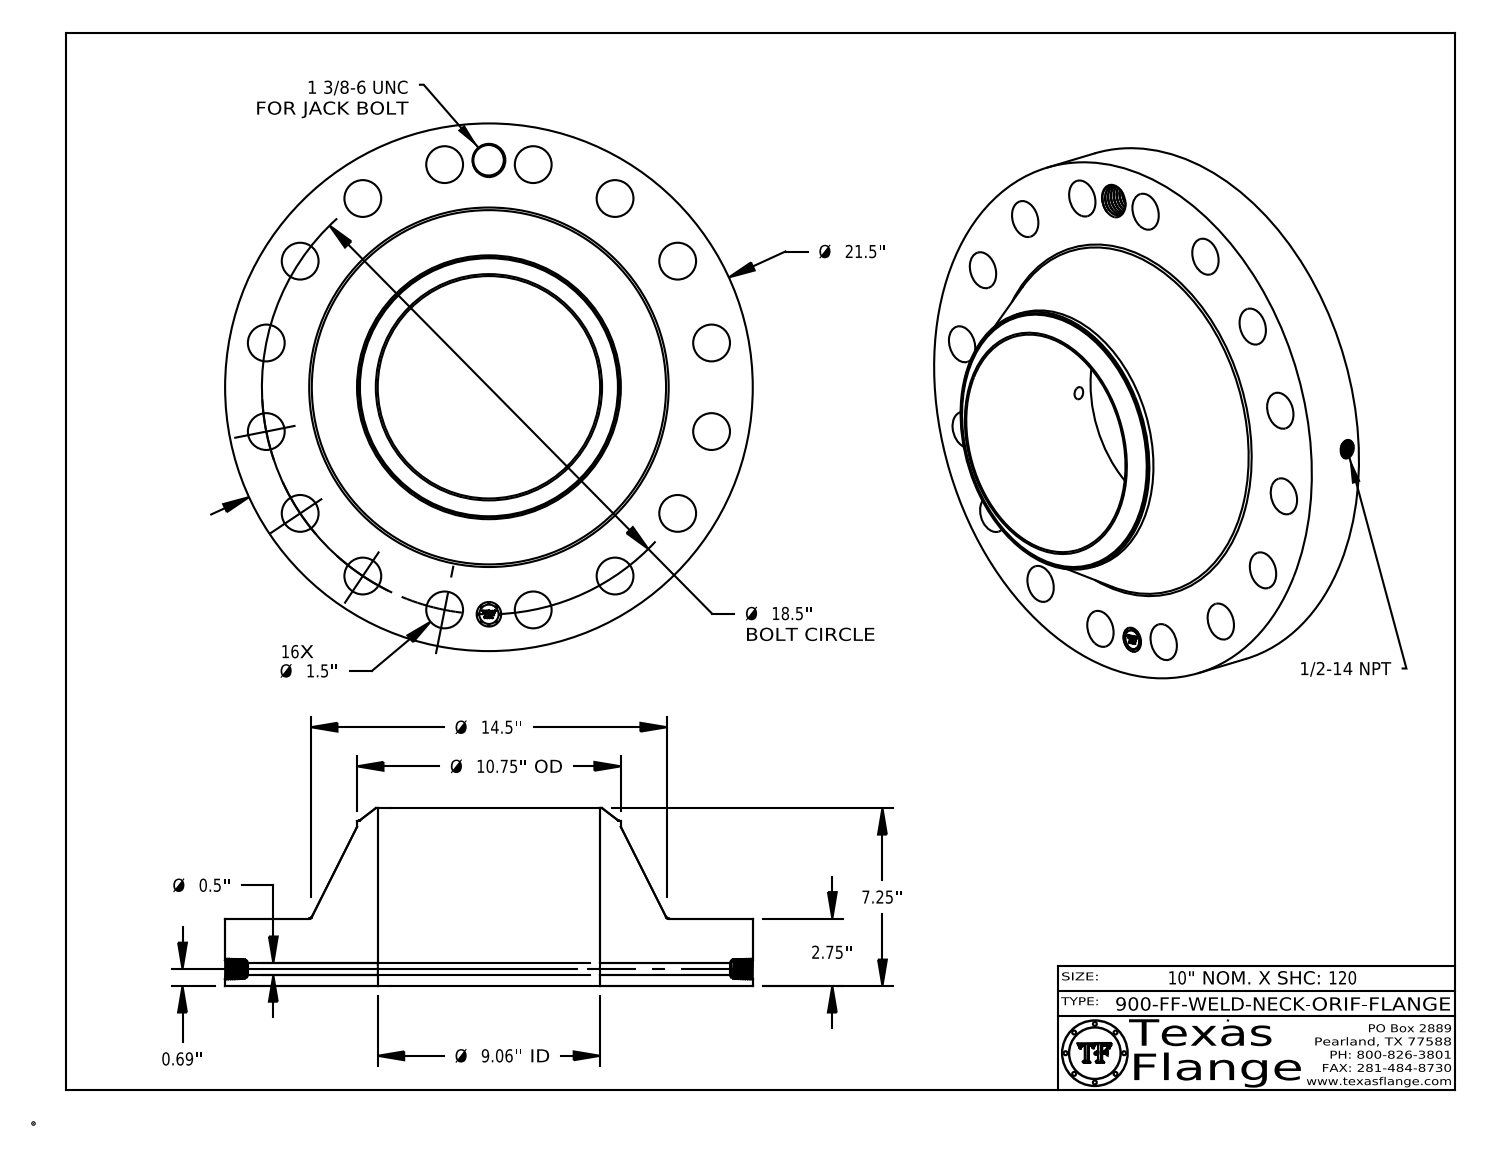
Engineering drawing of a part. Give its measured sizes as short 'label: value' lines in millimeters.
name: 900-FF-WELD-NECK
written by: CATIA V5 STEP AP214 (AUTOMOTIVE_DESIGN)
unit: mm
bodies: 1 solid, 795 faces (368 planar, 111 cylindrical, 316 other)
size: 546.1 × 546.1 × 184.2
volume: 16 060 000 mm³; area: 825 800 mm²
holes: 16× ⌀38.1, 1× ⌀12.7, 1× ⌀17.1, 1× ⌀25.4, 1× ⌀31, 1× ⌀230.2
bosses: 8× ⌀1.5, 1× ⌀546.1, 1× ⌀273.1, 1× ⌀20
face distances: 69.9, 184.2, 114.3, 69.5, 0.4, 114.7, 7.6, 7.4, 1.4, 6.3
hole spacings: 261.1, 434.1, 91.7, 235, 179.8, 179.8, 235, 332.3
